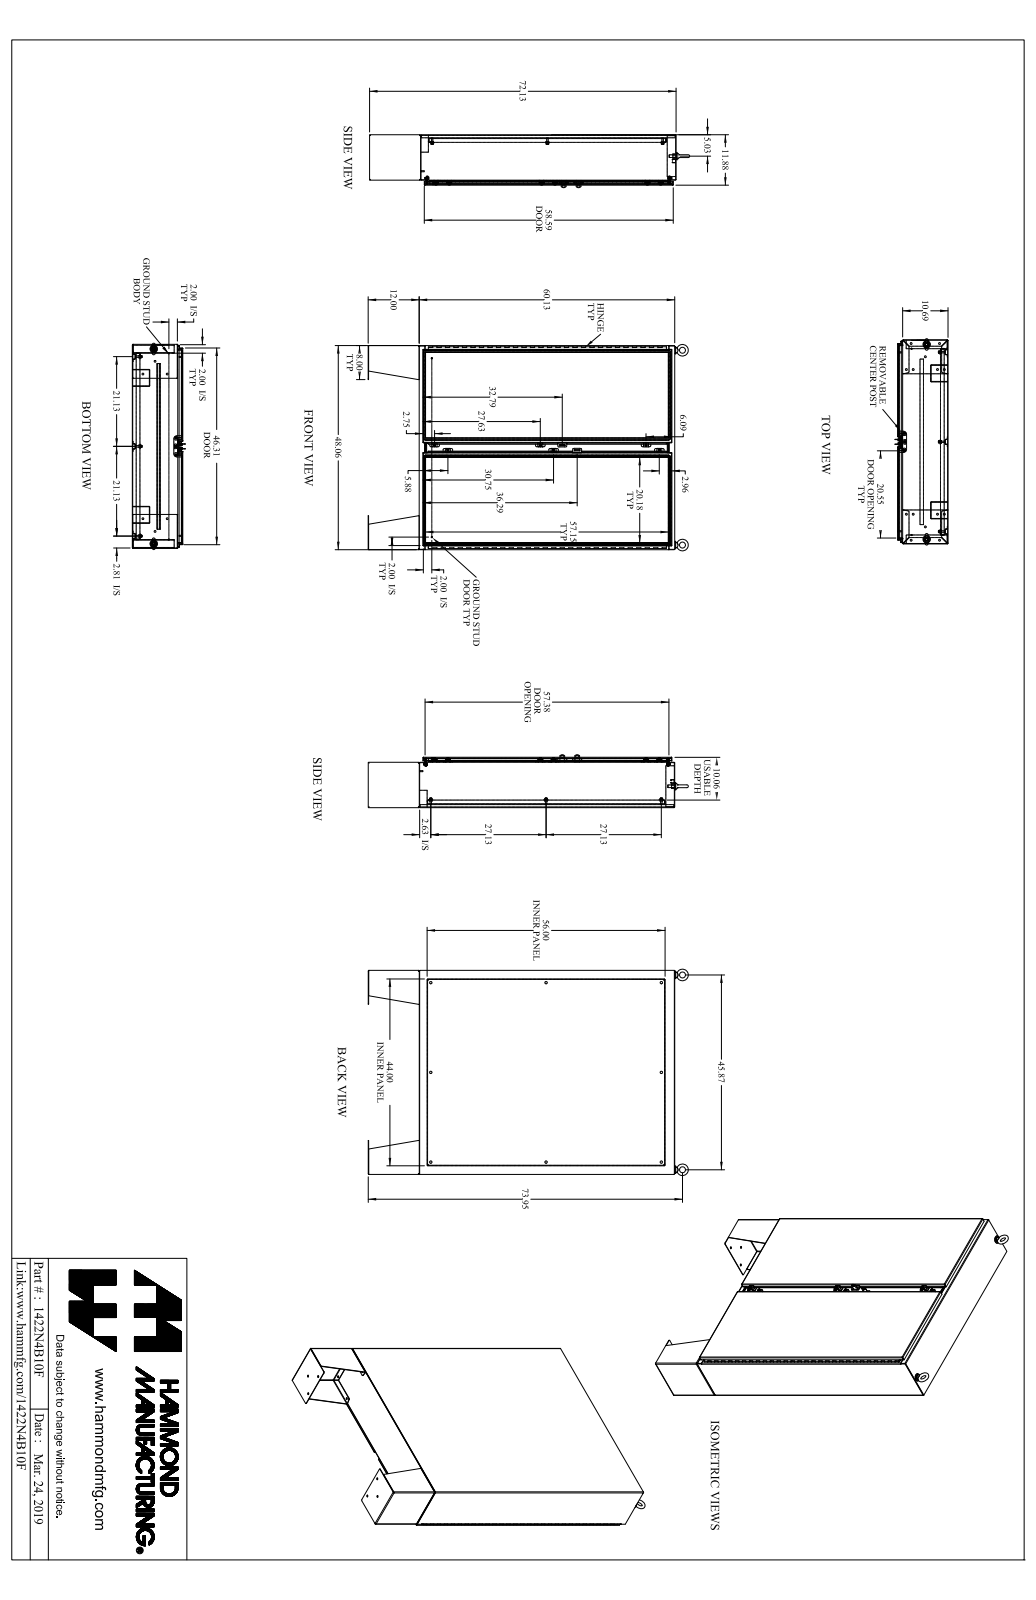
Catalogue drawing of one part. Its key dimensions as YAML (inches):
part_name: "1422N4B10F_Default"
step_written_by: "SolidWorks 2019 (CONFIG_CONTROL_DESIGN)"
units: inches
bodies: {solids: 107, faces: 3408, planar: 1754, cylindrical: 1442, other: 212}
overall_size: [75.778, 49.121, 12.468]
volume: 1380
surface_area: 27893
round_holes:
  - {diameter: 0.304, count: 20}
  - {diameter: 0.437, count: 14}
  - {diameter: 0.307, count: 8}
  - {diameter: 0.563, count: 8}
  - {diameter: 0.213, count: 6}
  - {diameter: 0.265, count: 6}
  - {diameter: 0.445, count: 6}
  - {diameter: 0.201, count: 3}
  - {diameter: 0.25, count: 3}
  - {diameter: 0.313, count: 3}
  - {diameter: 0.375, count: 3}
  - {diameter: 0.375, count: 3}
round_bosses_or_shafts:
  - {diameter: 1, count: 8}
  - {diameter: 0.65, count: 8}
  - {diameter: 0.375, count: 8}
  - {diameter: 0.33, count: 8}
  - {diameter: 0.5, count: 6}
  - {diameter: 0.39, count: 6}
  - {diameter: 0.244, count: 6}
  - {diameter: 0.281, count: 4}
partial_cylinders:
  - {radius: 0.048, count: 67}
  - {radius: 0.143, count: 67}
  - {radius: 0.25, count: 34}
  - {radius: 0.06, count: 18}
  - {radius: 0.116, count: 12}
  - {radius: 0.141, count: 12}
  - {radius: 0.185, count: 12}
  - {radius: 0.187, count: 9}
face_to_face_distances: [0.095, 11.78, 11.685, 9.998, 0.125, 11.875, 10.093, 1.687, 1.782, 10.218]
hole_center_spacings: [6, 46.593, 12, 47.737, 18, 49.587, 24, 52.066]
